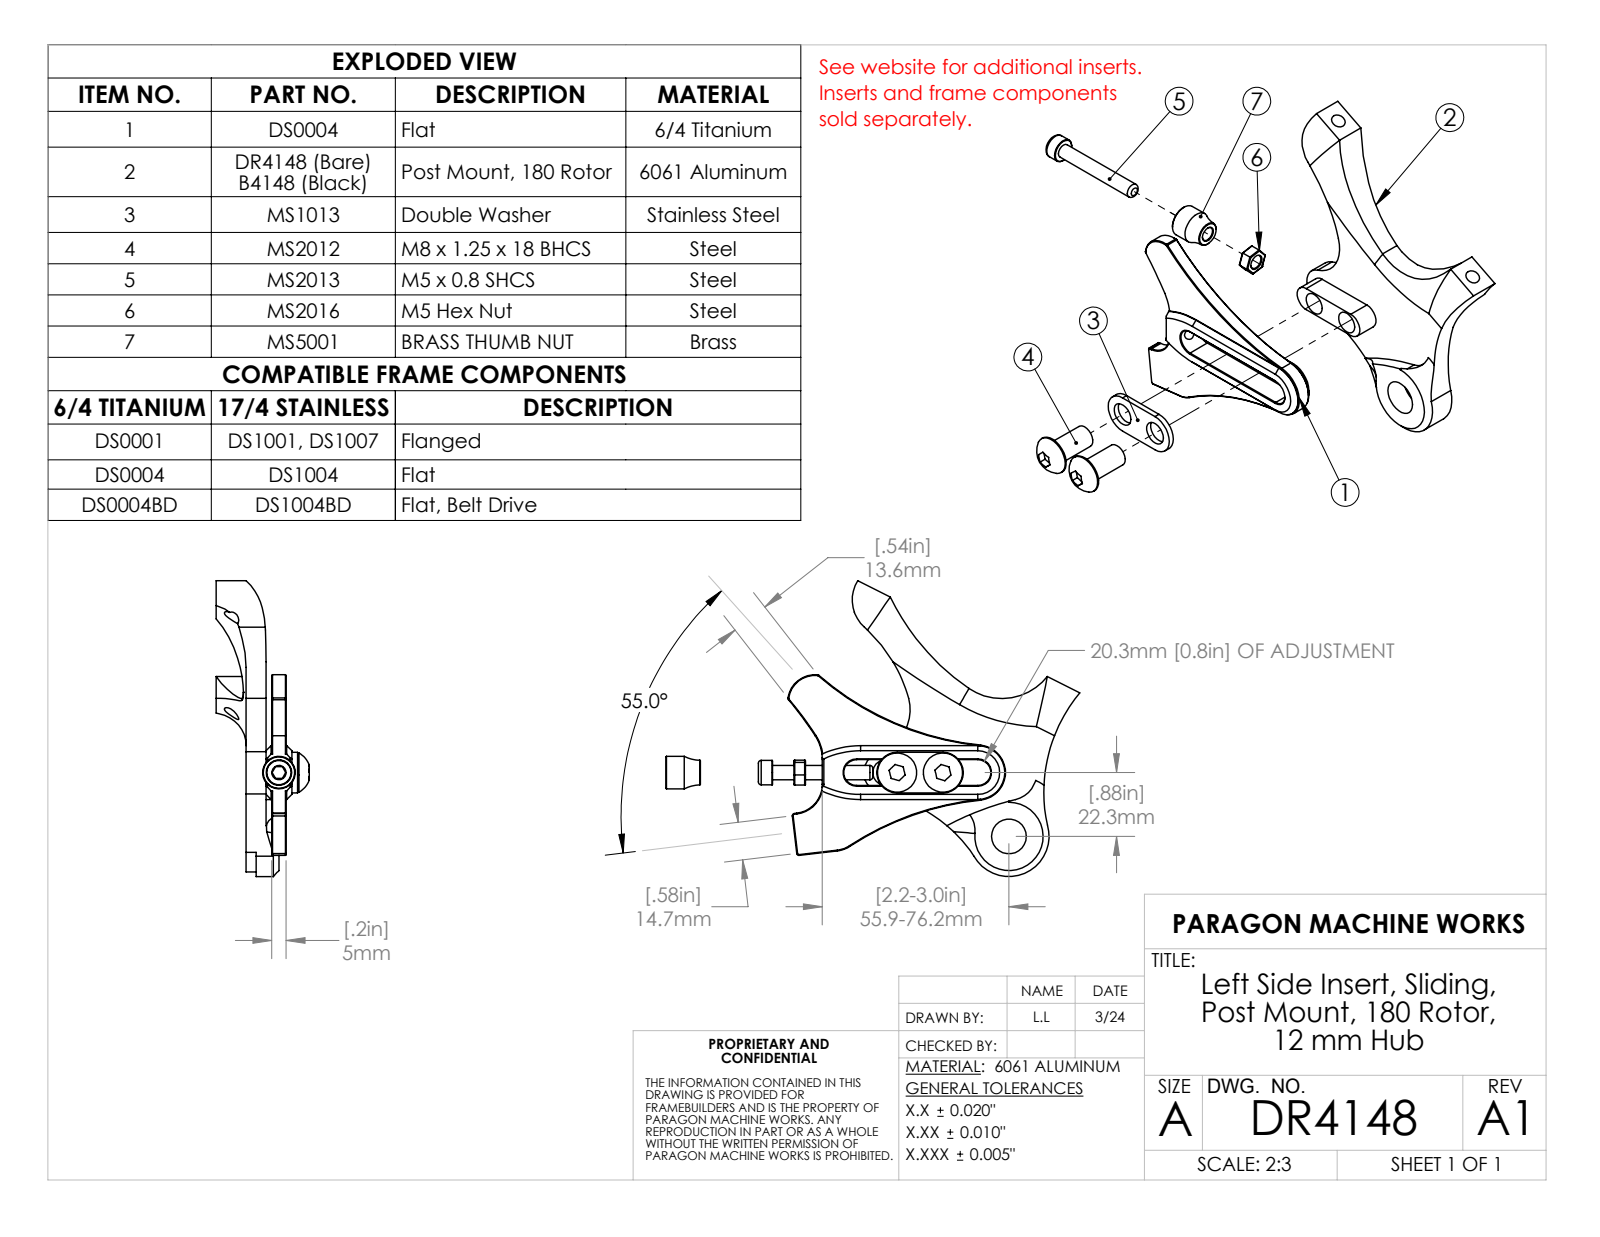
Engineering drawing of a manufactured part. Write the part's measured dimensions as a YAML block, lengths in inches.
part_name: "DR4148"
step_written_by: "SolidWorks 2023 (CONFIG_CONTROL_DESIGN)"
units: inches
bodies: {solids: 1, faces: 61, planar: 17, cylindrical: 34, other: 10}
overall_size: [4.45, 3.282, 1.047]
volume: 1.915
surface_area: 20.27
round_holes:
  - {diameter: 0.197, count: 2}
  - {diameter: 0.312, count: 2}
  - {diameter: 0.477, count: 1}
partial_cylinders:
  - {radius: 0.178, count: 2}
  - {radius: 0.5, count: 2}
  - {radius: 1, count: 2}
  - {radius: 0.3, count: 1}
  - {radius: 0.348, count: 1}
  - {radius: 0.385, count: 1}
  - {radius: 0.394, count: 1}
  - {radius: 0.46, count: 1}
face_to_face_distances: [0.274, 0.453, 0.179, 0.138, 0.136, 0.315, 0.46, 0.598, 0.734, 0.913]
hole_center_spacings: [0.63, 1.262, 1.77, 2.921]
